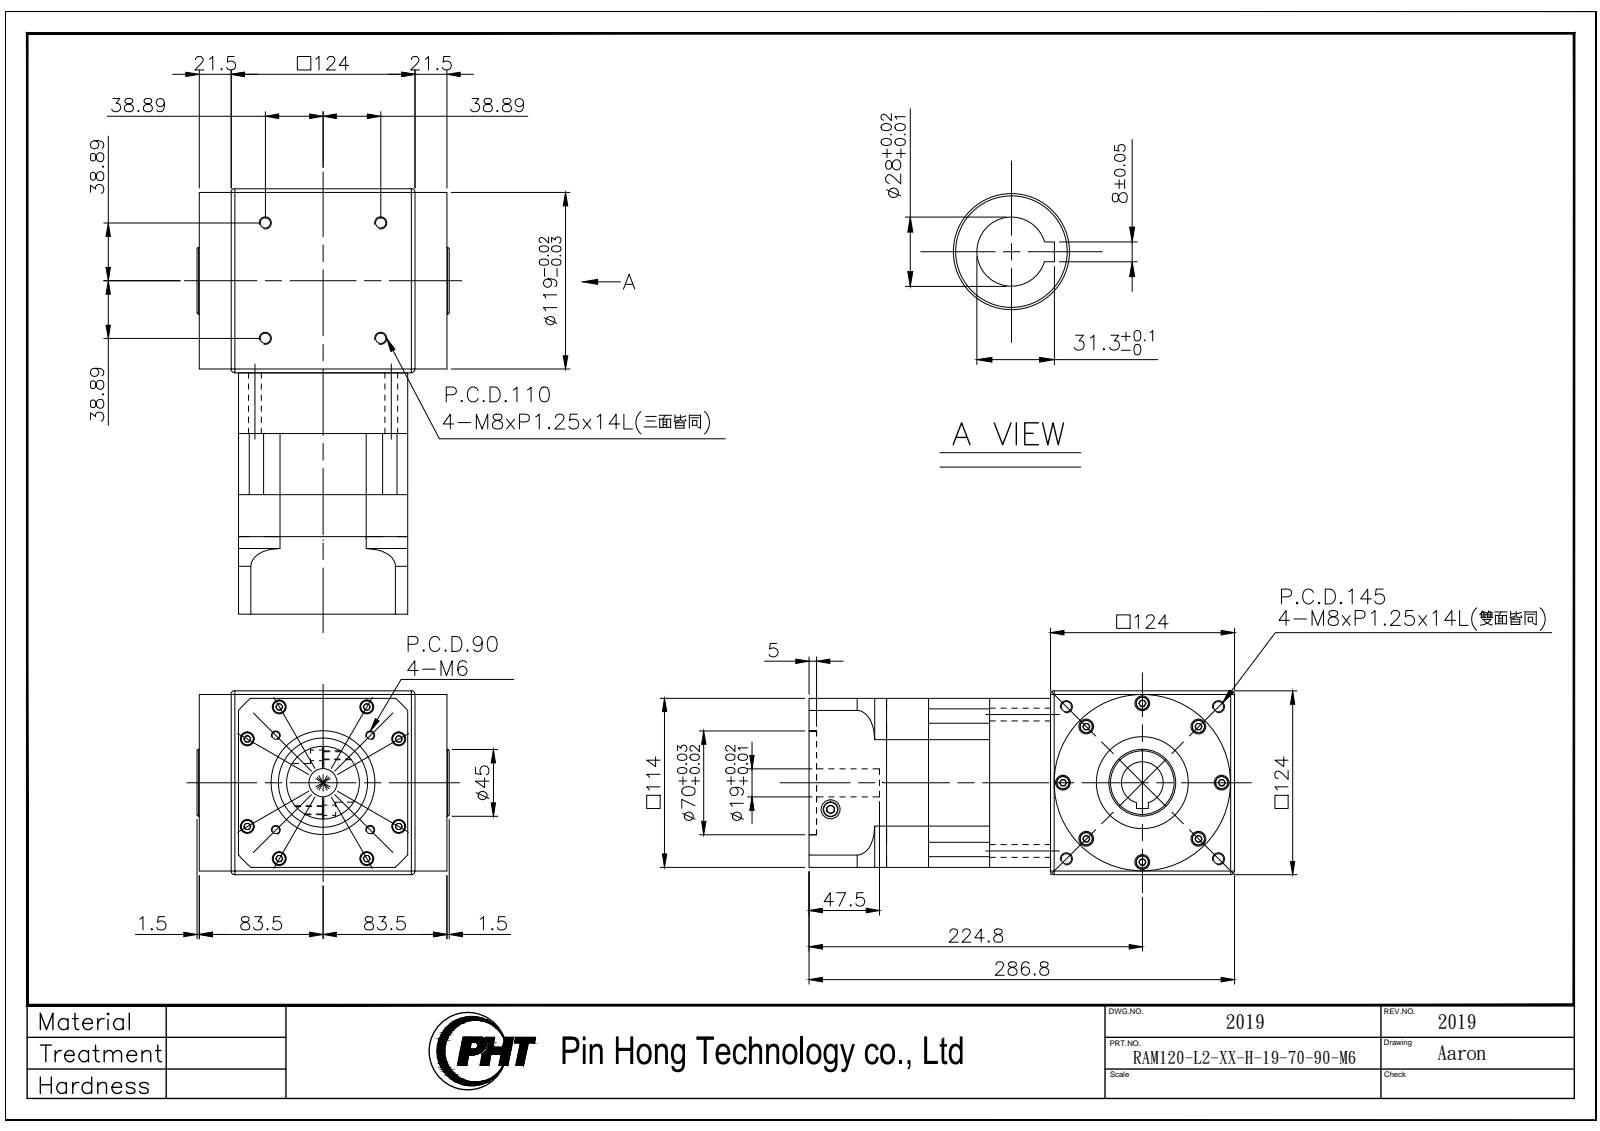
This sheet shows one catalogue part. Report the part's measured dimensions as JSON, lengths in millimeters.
{"part_name": "RAM120-L2-XX-H-19-70-90-M6_2019", "step_written_by": "SolidWorks 2016 (AUTOMOTIVE_DESIGN)", "units": "millimeters", "bodies": {"solids": 5, "faces": 854, "planar": 430, "cylindrical": 276, "other": 148}, "overall_size": [286.8, 170, 124], "volume_mm3": 4148000, "surface_area_mm2": 358894, "round_holes": [[6.8, 12], [5.3, 8], [9, 8], [9.5, 8], [14, 8], [5, 4], [8.6, 4], [12.7, 2], [19, 1], [28, 1], [28.3, 1], [60, 1]], "round_bosses_or_shafts": [[13, 12], [8.5, 8], [119, 1], [110, 1], [62, 1], [49, 1], [45, 1]], "partial_cylinders_radius": [[7, 4], [64, 1], [75, 1], [86.2, 1]], "face_to_face_distances": [5, 119, 124, 114, 69.5, 28.3, 41.2, 110.5, 82.2, 41], "hole_center_spacings": [59, 10, 15.4, 17.24, 19.42, 39.8, 51.28, 52]}
